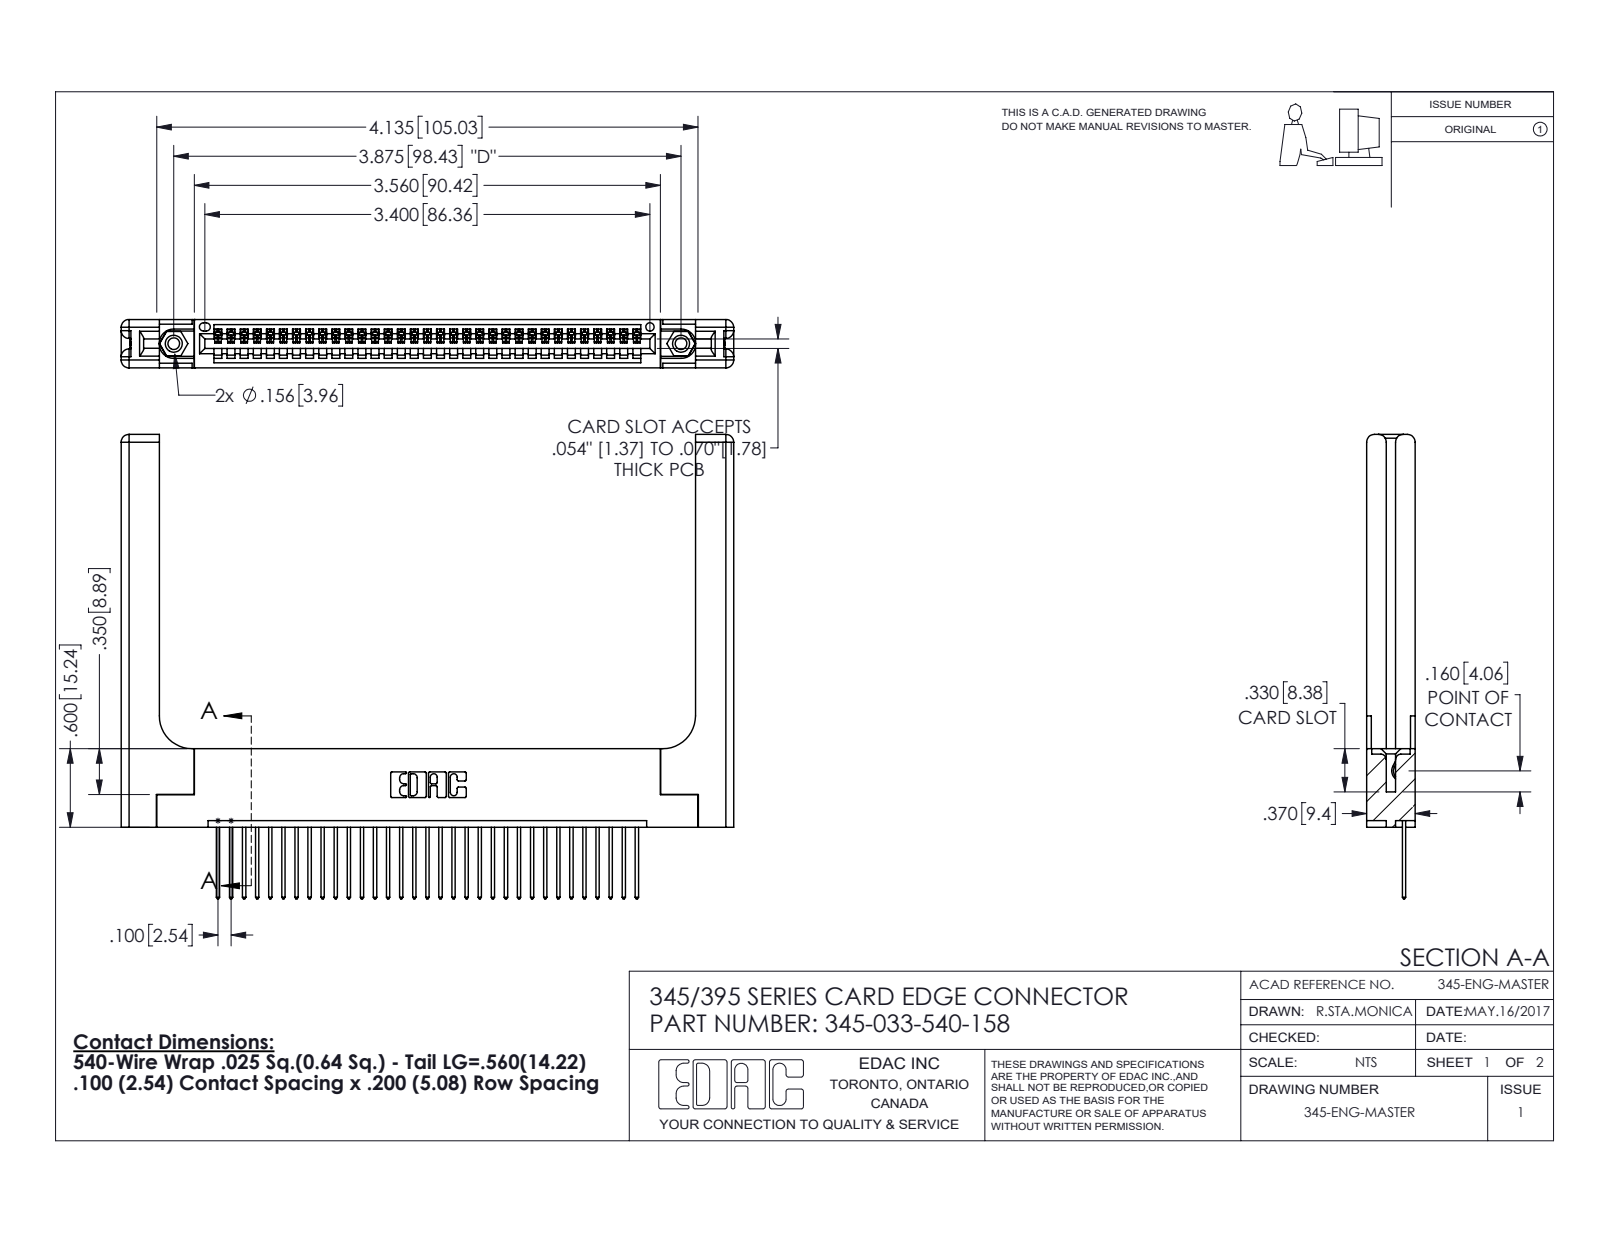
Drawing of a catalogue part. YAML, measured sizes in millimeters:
part_name: "345-220-058_345-220-058; 345-250-001_345-250-001-102; 345-292-001_345-293-140; 345 Part_Flush Mounting Lugs - 0.156 Dia-TH (+1 more)"
step_written_by: "SolidWorks 2016 (CONFIG_CONTROL_DESIGN)"
units: millimeters
bodies: {solids: 38, faces: 2296, planar: 1548, cylindrical: 688, other: 60}
overall_size: [118.8, 90.1, 9.4]
volume: 19760
surface_area: 20460
round_holes:
  - {diameter: 2.3, count: 2}
  - {diameter: 3.2, count: 2}
  - {diameter: 4, count: 2}
  - {diameter: 1.6, count: 1}
round_bosses_or_shafts:
  - {diameter: 3.9, count: 2}
partial_cylinders:
  - {radius: 0.2, count: 66}
  - {radius: 0.3, count: 66}
  - {radius: 0.3, count: 22}
  - {radius: 1.5, count: 16}
  - {radius: 0.2, count: 6}
  - {radius: 0.8, count: 6}
  - {radius: 0.7, count: 3}
  - {radius: 0.8, count: 2}
face_to_face_distances: [9.4, 1.8, 7.6, 5.1, 2.5, 6.9, 0.6, 3.8, 3.8, 2]
hole_center_spacings: [6.9, 92.5, 98.4]
